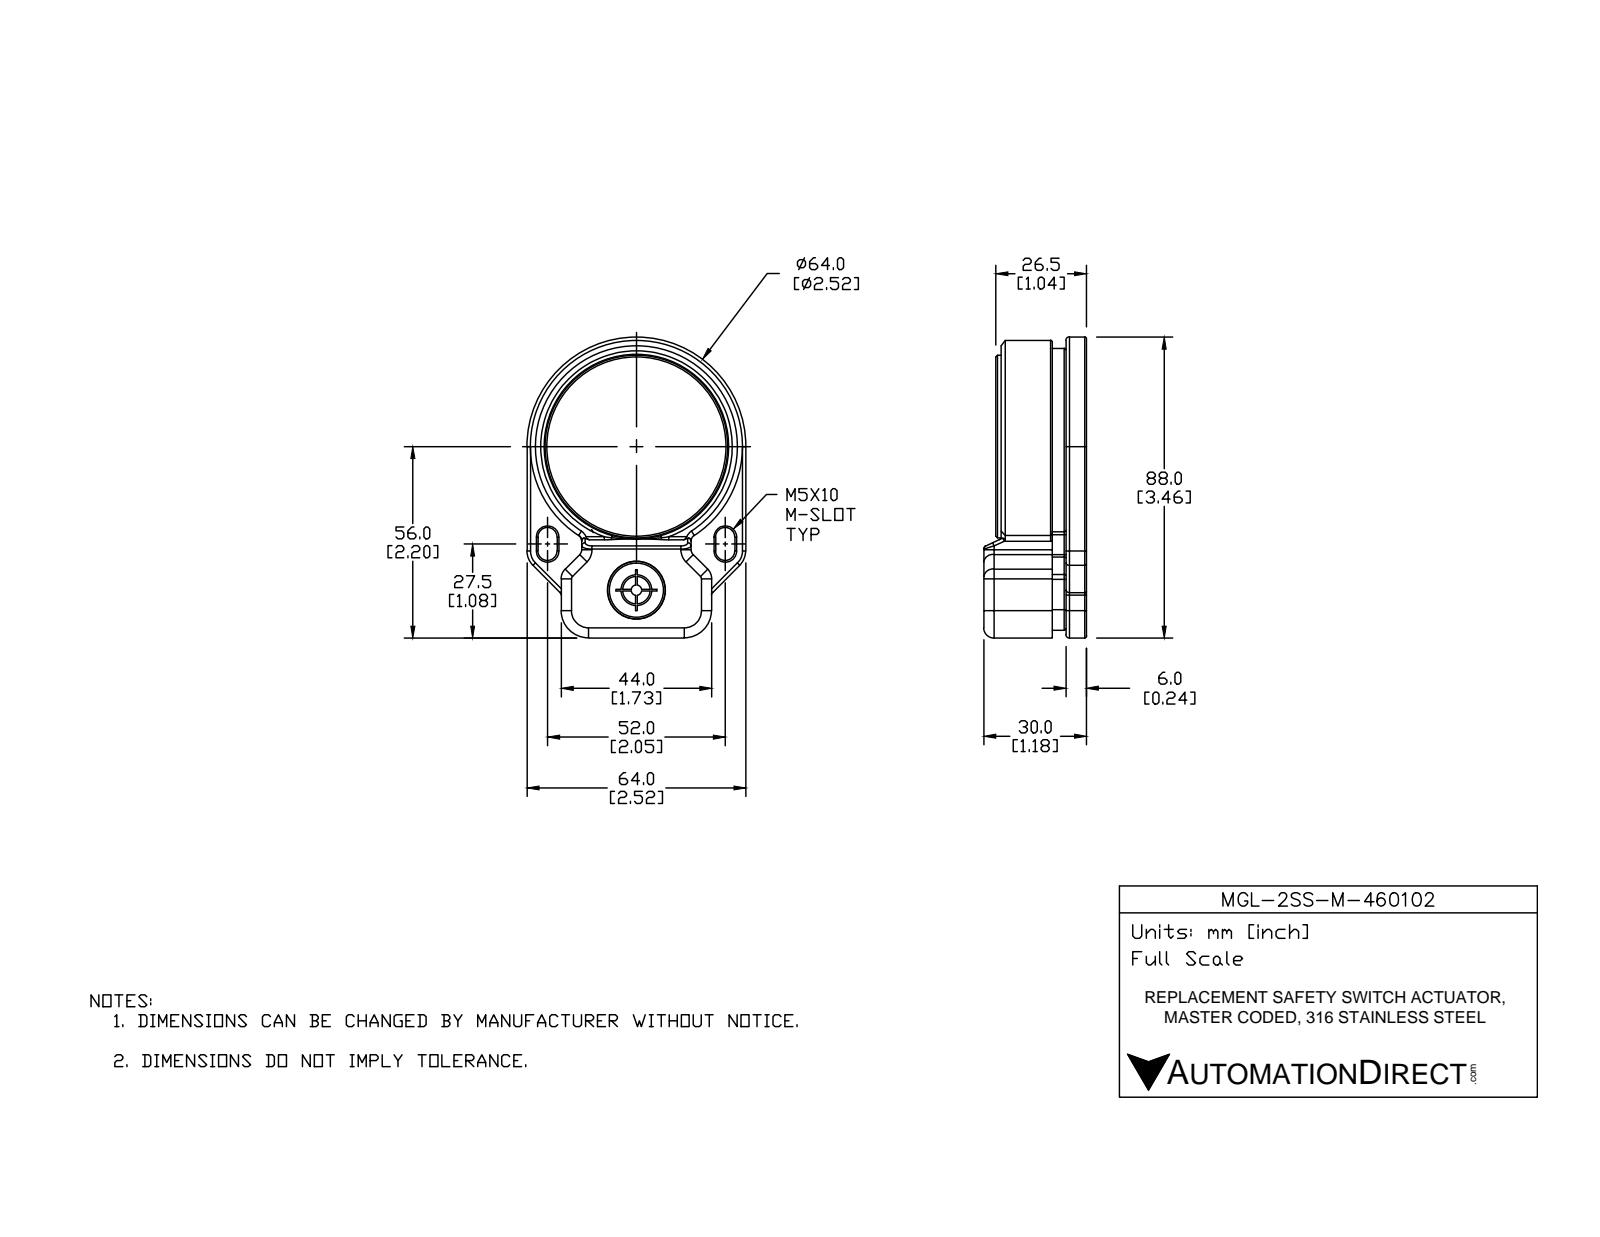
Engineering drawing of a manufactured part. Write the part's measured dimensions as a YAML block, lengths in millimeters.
part_name: "MGL-2SS-M-460102"
step_written_by: "SolidWorks 2017 (AUTOMOTIVE_DESIGN)"
units: millimeters
bodies: {solids: 7, faces: 754, planar: 158, cylindrical: 319, other: 277}
overall_size: [88, 64, 30]
volume: 82480
surface_area: 50620
round_holes:
  - {diameter: 8, count: 6}
  - {diameter: 2.5, count: 2}
  - {diameter: 3.3, count: 2}
  - {diameter: 4, count: 2}
  - {diameter: 5, count: 2}
  - {diameter: 9, count: 2}
  - {diameter: 17, count: 2}
  - {diameter: 6.7, count: 1}
  - {diameter: 8.2, count: 1}
  - {diameter: 10, count: 1}
  - {diameter: 10.5, count: 1}
  - {diameter: 20, count: 1}
round_bosses_or_shafts:
  - {diameter: 62, count: 1}
  - {diameter: 57.4, count: 1}
  - {diameter: 53.4, count: 1}
  - {diameter: 23, count: 1}
  - {diameter: 16.8, count: 1}
  - {diameter: 14, count: 1}
  - {diameter: 13, count: 1}
  - {diameter: 10.2, count: 1}
partial_cylinders:
  - {radius: 0.5, count: 92}
  - {radius: 1, count: 36}
  - {radius: 2, count: 24}
  - {radius: 3, count: 9}
  - {radius: 0.6, count: 7}
  - {radius: 6, count: 6}
  - {radius: 2.8, count: 4}
  - {radius: 4, count: 3}
face_to_face_distances: [10.5, 16.5, 6, 2.5, 12.5, 10, 1.5, 7.5, 8, 6.5]
hole_center_spacings: [19.5, 27.6, 9.6, 13.9, 14.7, 22.8, 28.6, 30.4]
